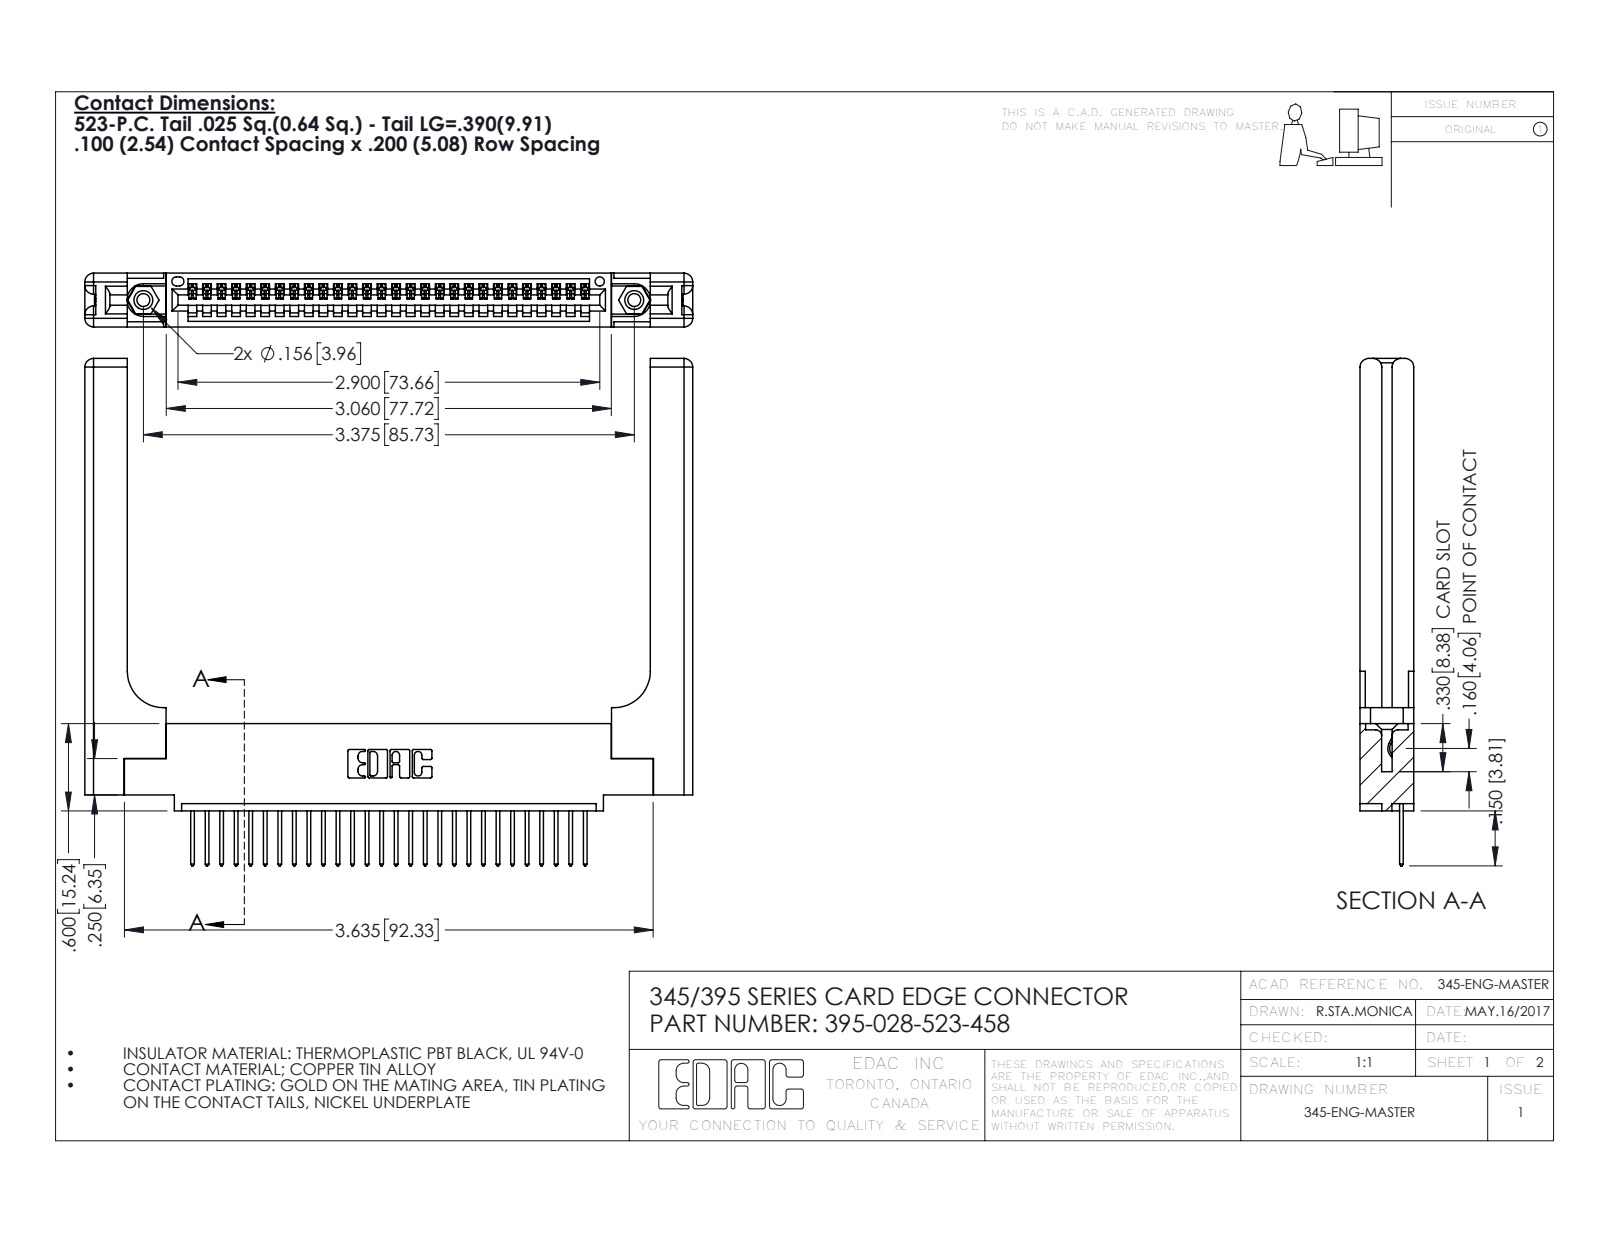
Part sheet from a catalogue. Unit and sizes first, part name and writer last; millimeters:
Units: millimetres
Overall size (bounding box): 106.1 × 88.6 × 9.4
Round holes (diameter × count): ⌀2.3 ×2, ⌀3.2 ×2, ⌀4 ×2, ⌀1.6 ×1
Round bosses / shafts (diameter × count): ⌀3.9 ×2
Partial cylindrical surfaces — rounded edges, fillets, slot ends (radius × count): R0.2 ×56, R0.3 ×56, R0.3 ×22, R1.5 ×16, R0.2 ×6, R0.8 ×6, R0.7 ×3, R0.8 ×2
Main face-to-face distances: 9.4, 1.8, 7.6, 2.5, 6.9, 0.6, 5.1, 3.8, 3.8, 2
Hole centre spacings: 6.9, 79.8, 85.7
Volume: 18 390 mm³ · Surface area: 18 360 mm²
Bodies: 33 solids, 2010 faces (1352 planar, 598 cylindrical, 60 other)
Part name (STEP PRODUCT): 345-292-001_345-293-123; 345 Part_0.110 Offset - 0.156 Dia-TH; 395-028-523-458; 345-220-058_345-220-058 (+1 more)
STEP written by: SolidWorks 2016 (CONFIG_CONTROL_DESIGN)
